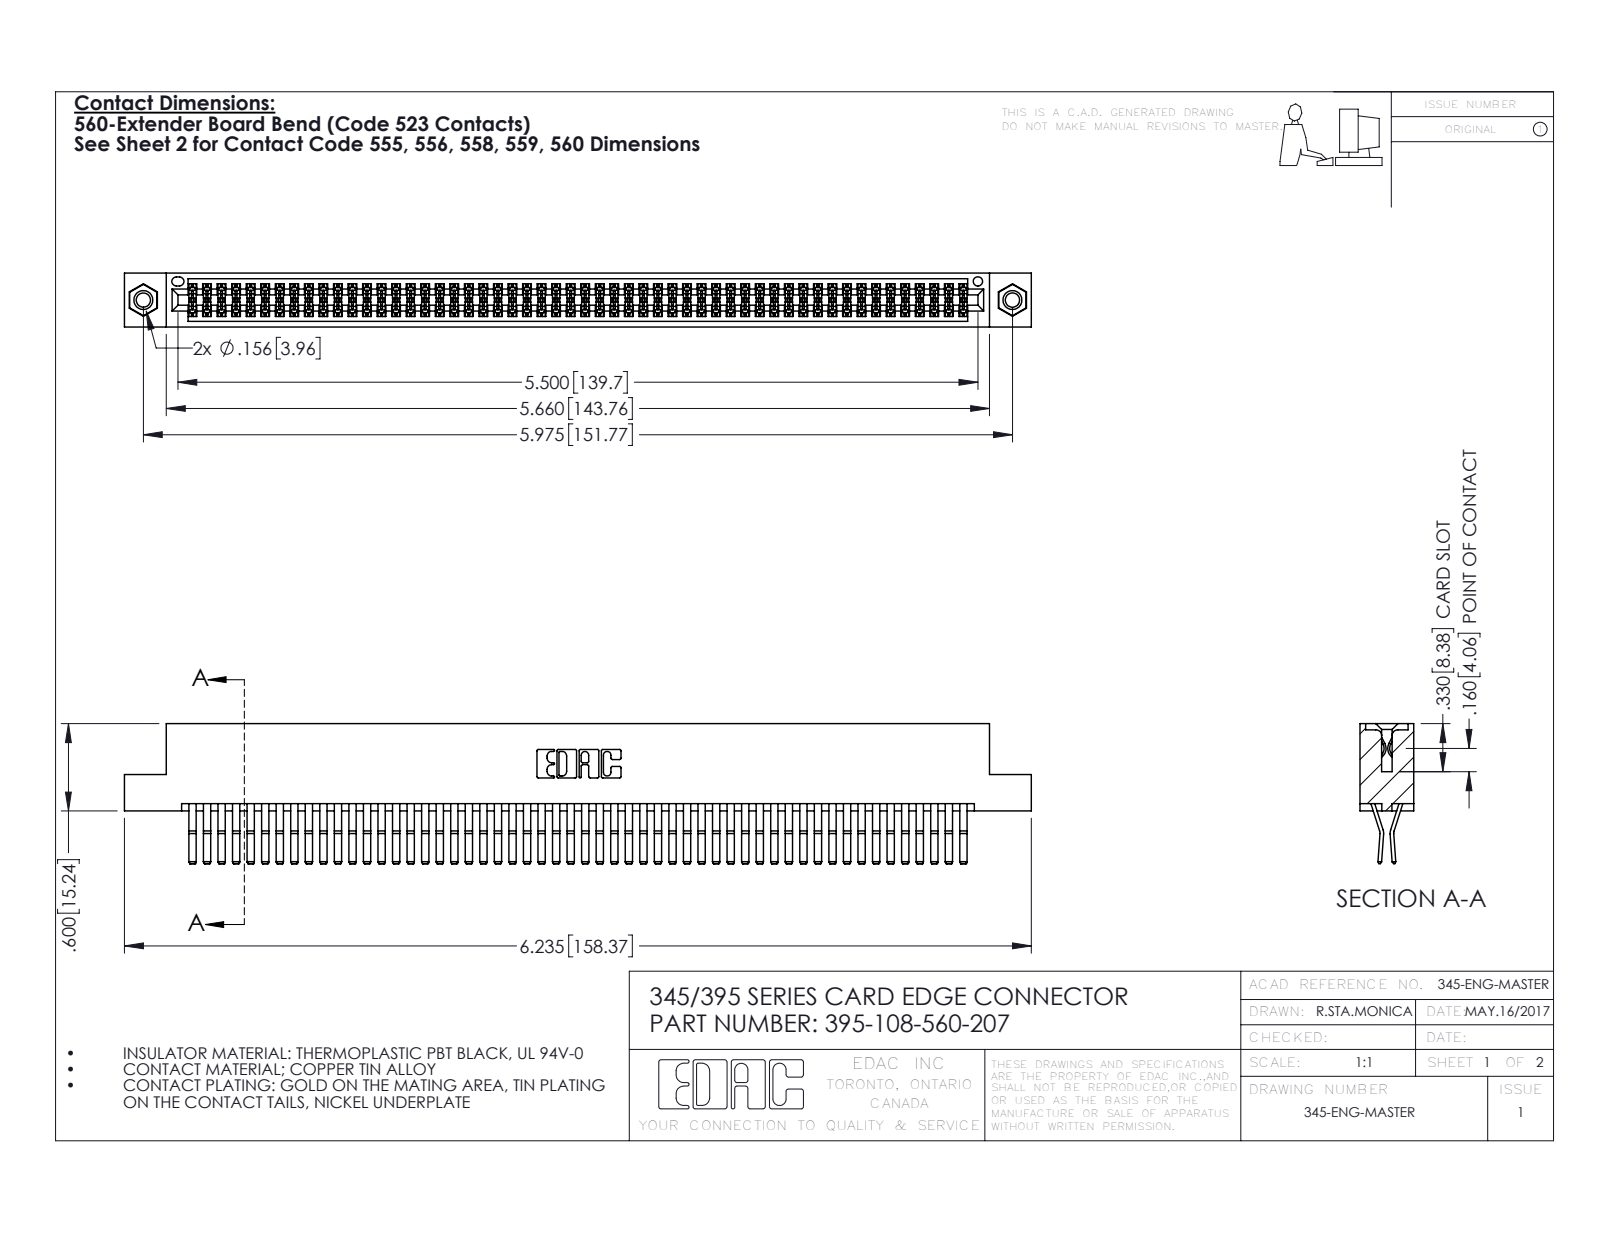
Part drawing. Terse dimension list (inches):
name: 345-292-001_560 Tail; 345-250-001_345-250-005-103; 345 Part_Flush Mounting Lugs - 0.156 Dia-TI; 395-108-560-207
written by: SolidWorks 2016 (CONFIG_CONTROL_DESIGN)
unit: in
bodies: 111 solids, 5802 faces (3676 planar, 2110 cylindrical, 16 other)
size: 6.235 × 0.962 × 0.37
volume: 0.988 in³; area: 40.32 in²
holes: 2× ⌀0.098, 2× ⌀0.125, 2× ⌀0.156, 1× ⌀0.064
bosses: 2× ⌀0.155
rounds: 162× R0.006, 22× R0.01, 6× R0.007, 6× R0.031, 3× R0.026, 2× R0.01, 2× R0.014, 2× R0.019
face distances: 0.025, 0.072, 0.298, 0.37, 0.2, 0.098, 0.272, 0.225, 0.175, 0.149
hole spacings: 0.27, 5.739, 5.975
